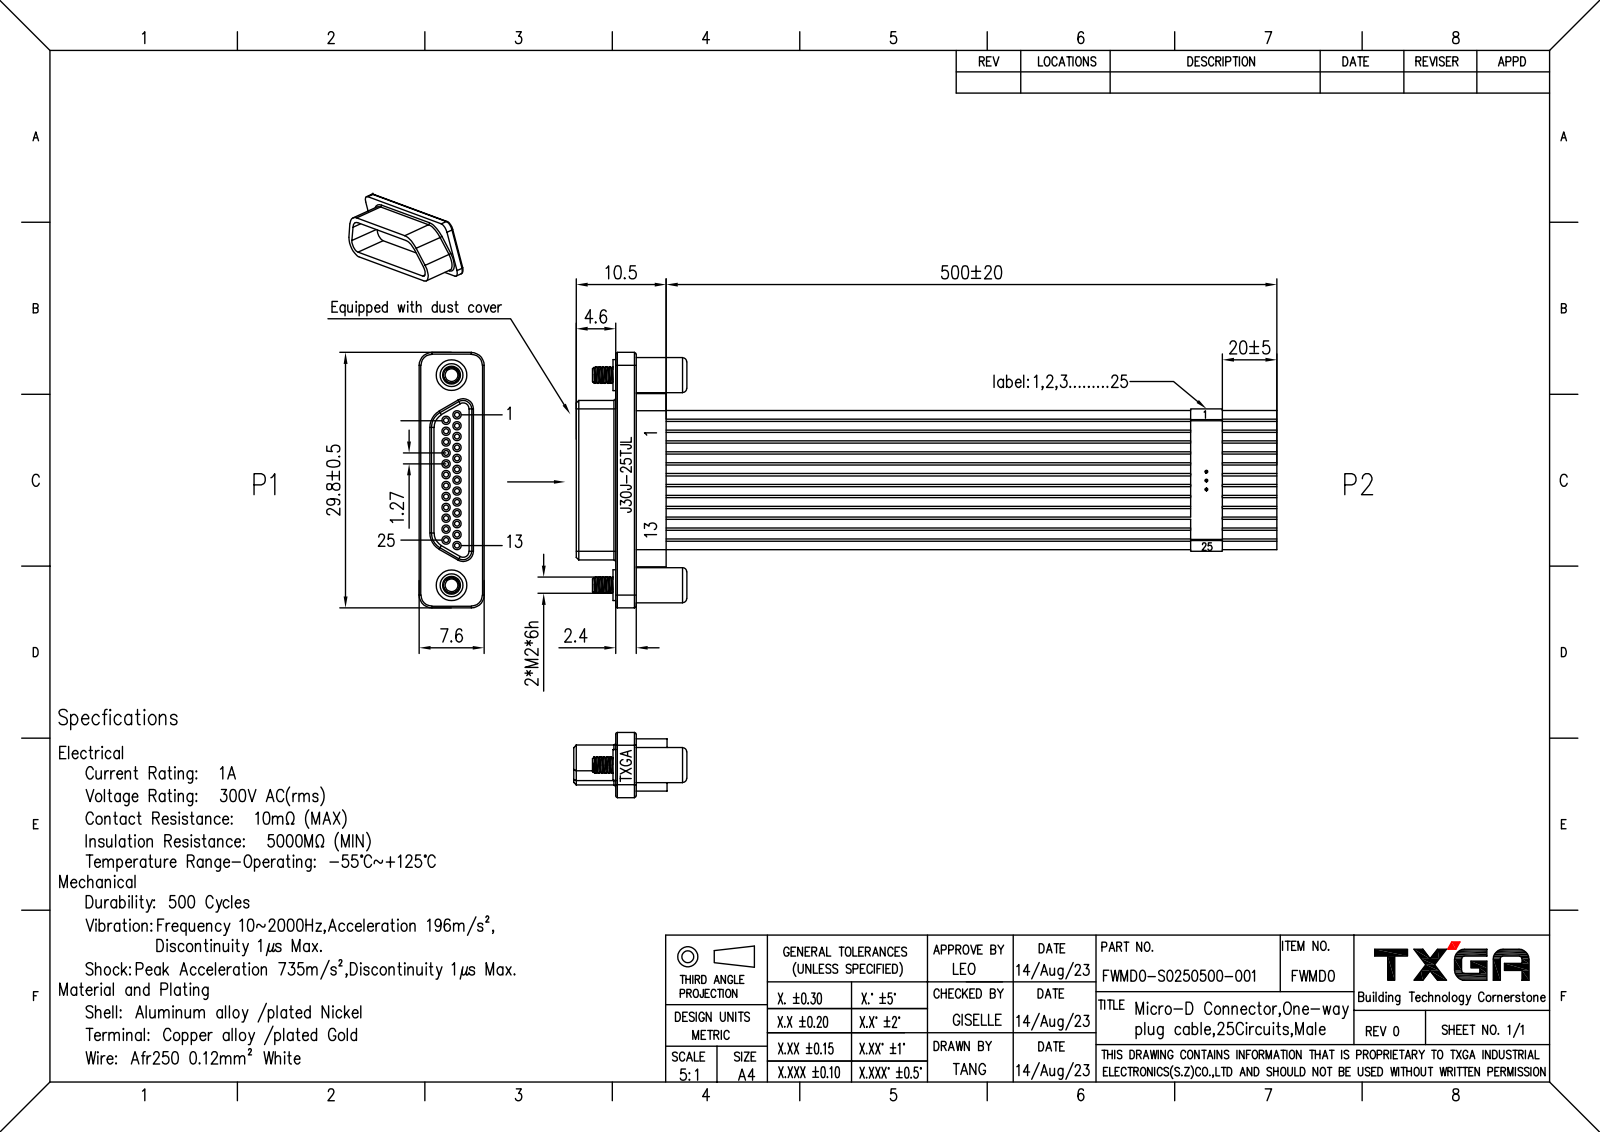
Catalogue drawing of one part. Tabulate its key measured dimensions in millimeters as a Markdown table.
| quantity | value |
| --- | --- |
| part name | ZHUTI-25P; PINZHEN-251; PINZHEN-252; LUOSISHELL (+3 more) |
| STEP written by | PRO/ENGINEER BY PARAMETRIC TECHNOLOGY CORPORATION, 2010280 (CONFIG_CONTROL_DESIGN) |
| units | millimeters |
| bodies | 55 solids, 830 faces (354 planar, 346 cylindrical, 130 other) |
| overall size | 110.5 × 29.8 × 7.6 |
| volume | 3 592 mm³ |
| surface area | 11 472 mm² |
| round holes (diameter × count) | 1 × 25, 2.1 × 2, 2.8 × 2, 3.25 × 2, 3.5 × 2 |
| round bosses / shafts (diameter × count) | 0.6 × 25, 1.05 × 13, 1.05 × 12, 4.1 × 2, 3.6 × 2, 3.2 × 2, 1.9 × 2 |
| partial cylindrical surfaces (radius × count) | 0.2 × 28, 1.2 × 4, 1.5 × 4, 2 × 4, 0.7 × 2, 1 × 2, 1.9 × 2, 2.2 × 2 |
| main face-to-face distances | 1.05, 5.75, 0.4, 1.45, 6.15, 7.2, 6.8, 5.6, 3.2, 2.4 |
| hole center spacings | 1.43, 2.54, 1.27, 3.81, 5.08, 2.3, 6.35, 7.62 |
